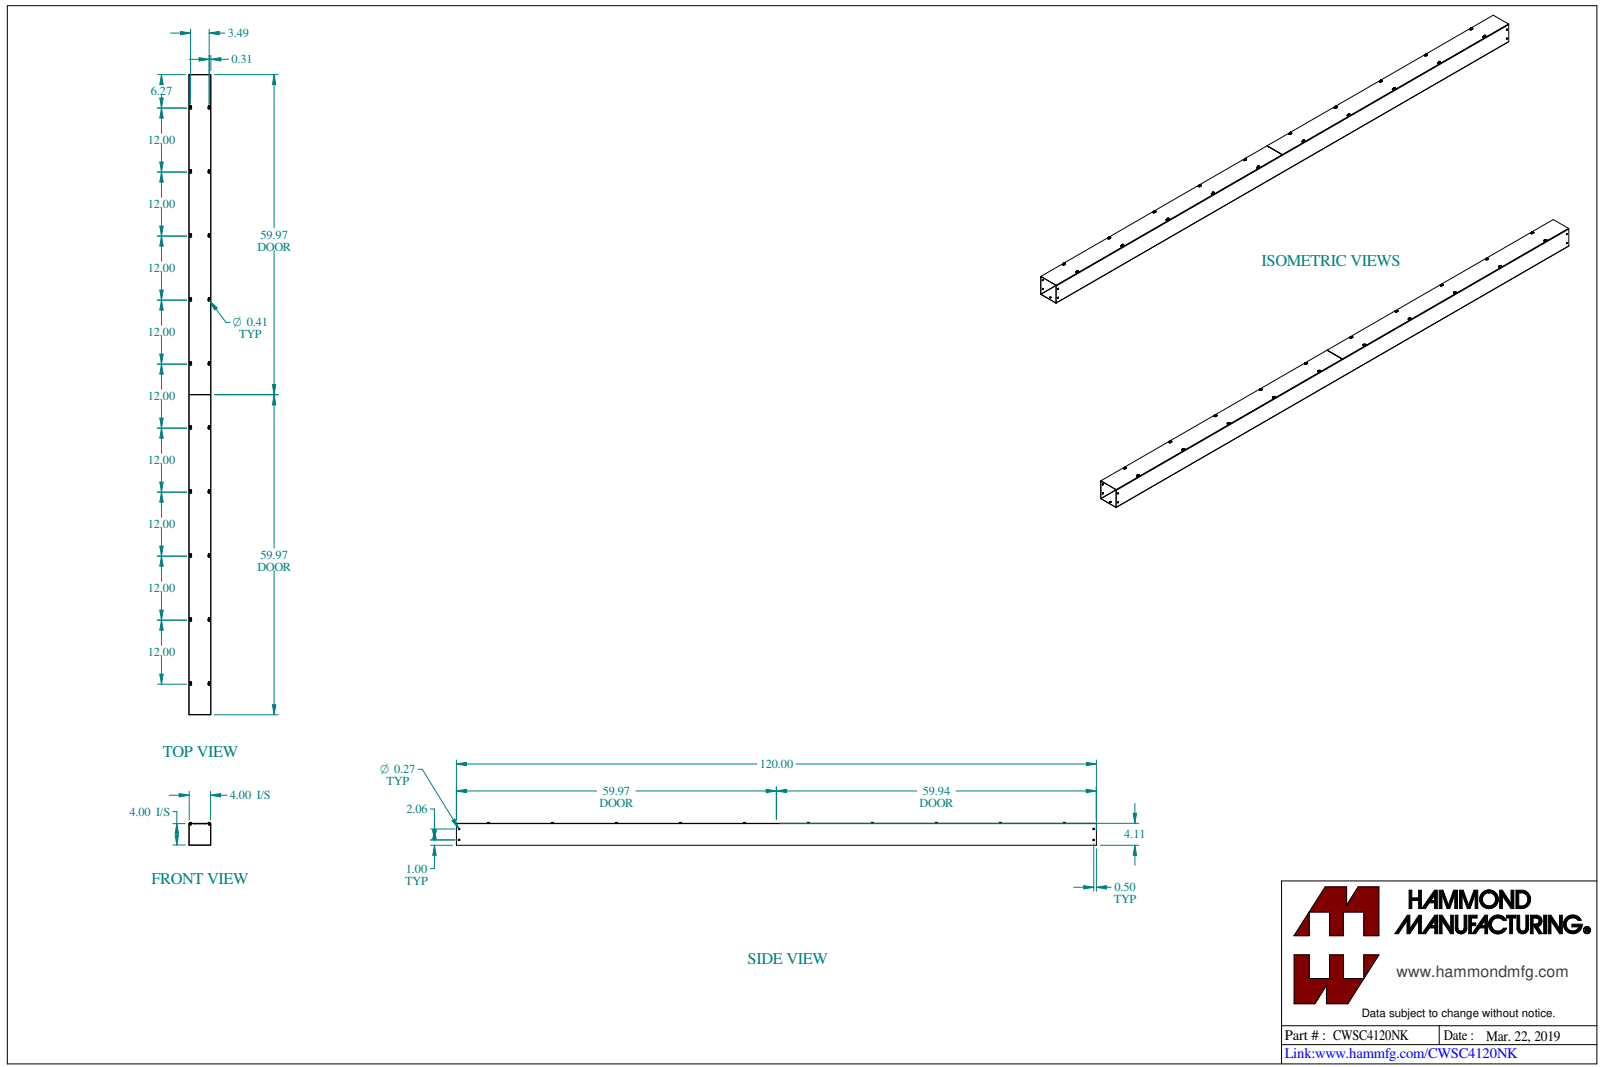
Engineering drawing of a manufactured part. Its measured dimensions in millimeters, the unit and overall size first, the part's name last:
Units: millimetres
Overall size (bounding box): 3048 × 108.9 × 104.5
Round holes (diameter × count): ⌀4.5 ×20, ⌀6.8 ×4, ⌀8 ×2
Round bosses / shafts (diameter × count): ⌀9.5 ×20, ⌀4.8 ×20
Partial cylindrical surfaces — rounded edges, fillets, slot ends (radius × count): R3.2 ×20, R5.2 ×20, R0.7 ×4, R2.2 ×4
Main face-to-face distances: 1.4, 103, 101.6, 104.5, 100.2, 2.9, 0.8, 103.7, 0.7, 102.3
Hole centre spacings: 304.8, 317.4, 609.6, 616, 914.4, 918.7, 1219.2, 1222.4
Volume: 1 903 000 mm³ · Surface area: 2 646 000 mm²
Bodies: 23 solids, 682 faces (334 planar, 228 cylindrical, 120 other)
Part name (STEP PRODUCT): CWSC4120NK
STEP written by: SolidWorks 2023 (CONFIG_CONTROL_DESIGN)
